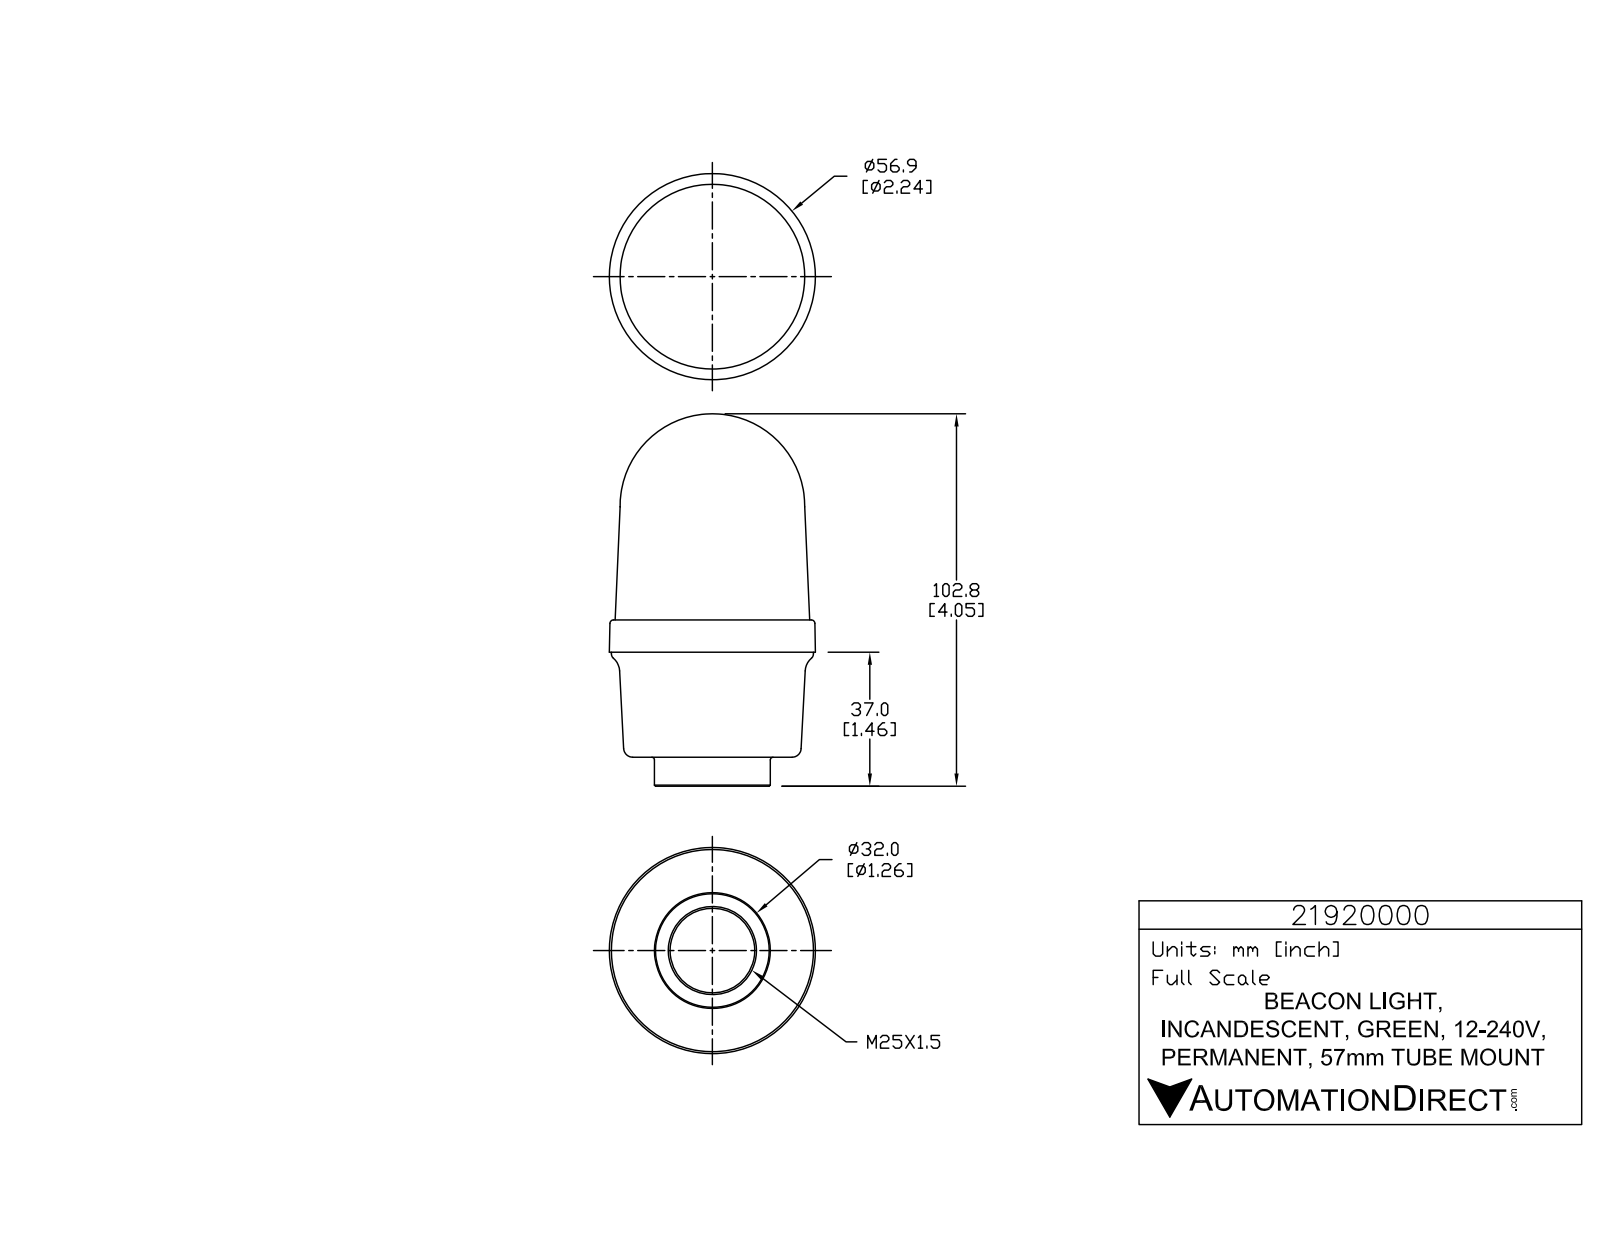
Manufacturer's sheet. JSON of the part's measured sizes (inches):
{"part_name": "21920000", "step_written_by": "SolidWorks 2015 (AUTOMOTIVE_DESIGN)", "units": "inches", "bodies": {"solids": 1, "faces": 764, "planar": 524, "cylindrical": 145, "other": 95}, "overall_size": [4.047, 2.24, 2.24], "volume_in3": 11.36, "surface_area_in2": 29.4, "round_holes": [[0.039, 3], [0.92, 1]], "round_bosses_or_shafts": [[0.226, 3], [0.056, 3], [2.197, 1], [1.26, 1]], "partial_cylinders_radius": [[0.008, 6], [0.008, 6], [0.008, 6], [0.131, 6], [0.004, 3], [0.005, 3], [0.007, 3], [0.008, 3]], "face_to_face_distances": [0.315, 1.142, 1.457, 0.35, 1.492, 1.807, 0.418, 0.768, 1.91, 2.225]}
